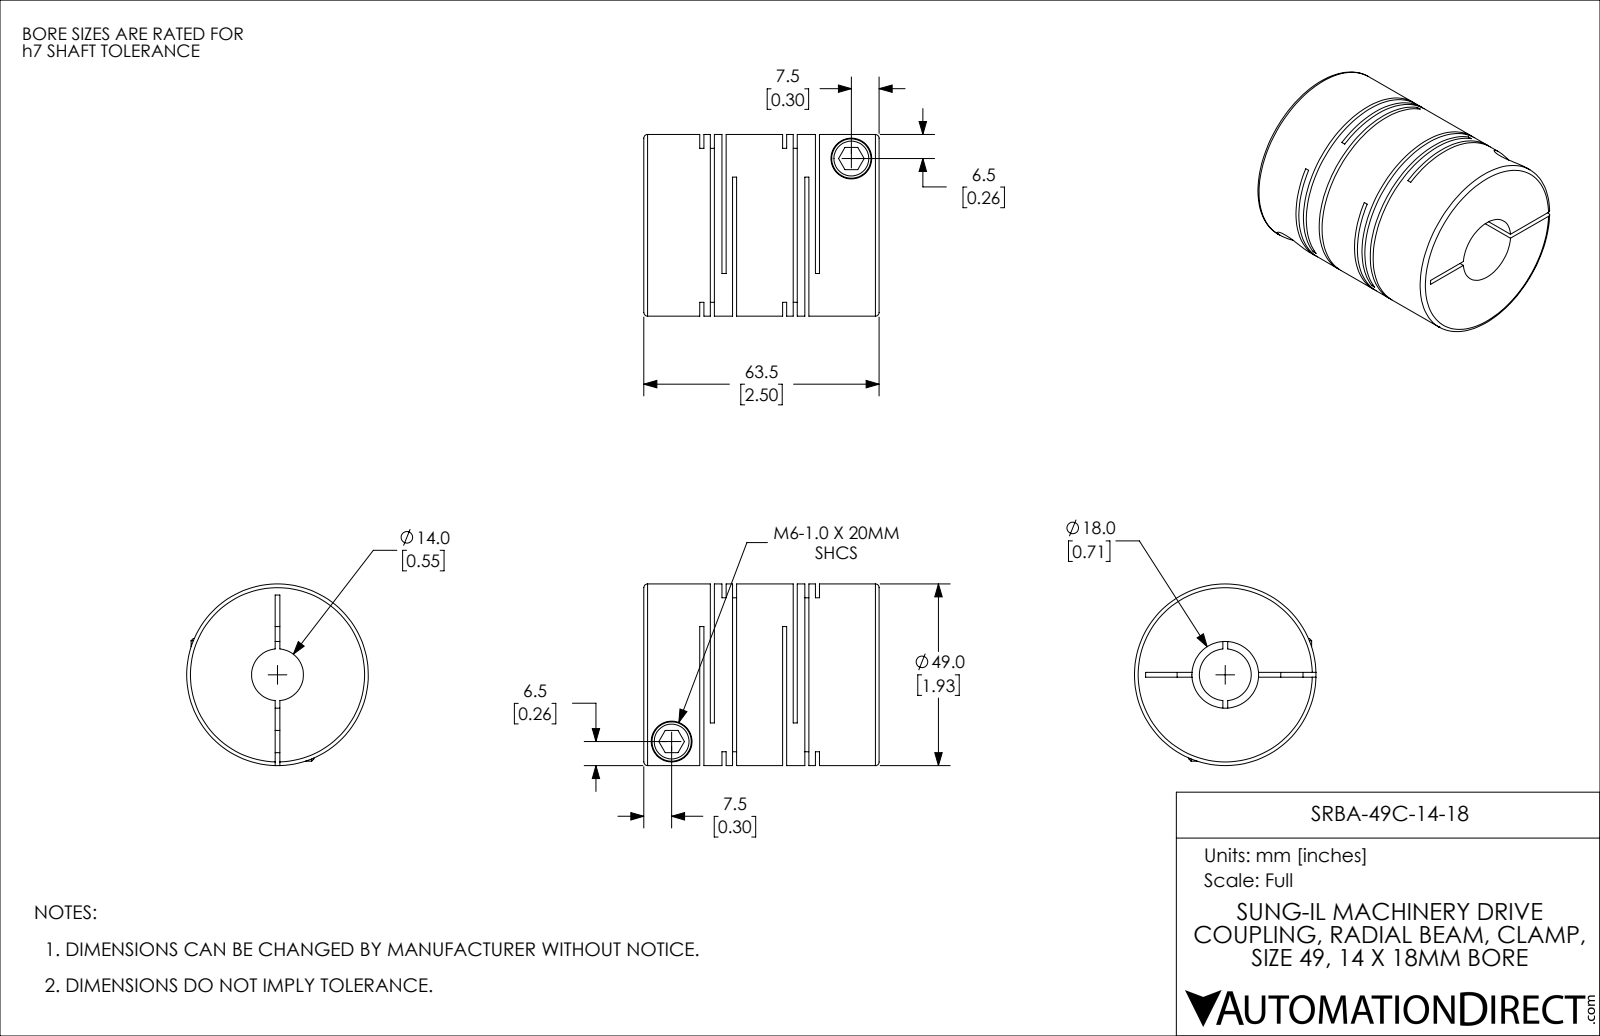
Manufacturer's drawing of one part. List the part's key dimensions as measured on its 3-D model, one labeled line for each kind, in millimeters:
Part name (STEP PRODUCT): SRBA-49C-14-18
STEP written by: SolidWorks 2021 (CONFIG_CONTROL_DESIGN)
Units: millimetres
Bodies: 1 solid, 114 faces (60 planar, 42 cylindrical, 12 other)
Overall size (bounding box): 63.5 × 49 × 49
Volume: 90 853 mm³ · Surface area: 38 936 mm²
Round holes (diameter × count): ⌀6 ×2, ⌀11 ×2, ⌀14 ×1, ⌀18 ×1
Round bosses / shafts (diameter × count): ⌀10.6 ×2, ⌀49 ×1
Main face-to-face distances: 6, 1.1, 2.85, 22.35, 4.9, 21.25, 3.15, 19.5, 16.35, 1.75
